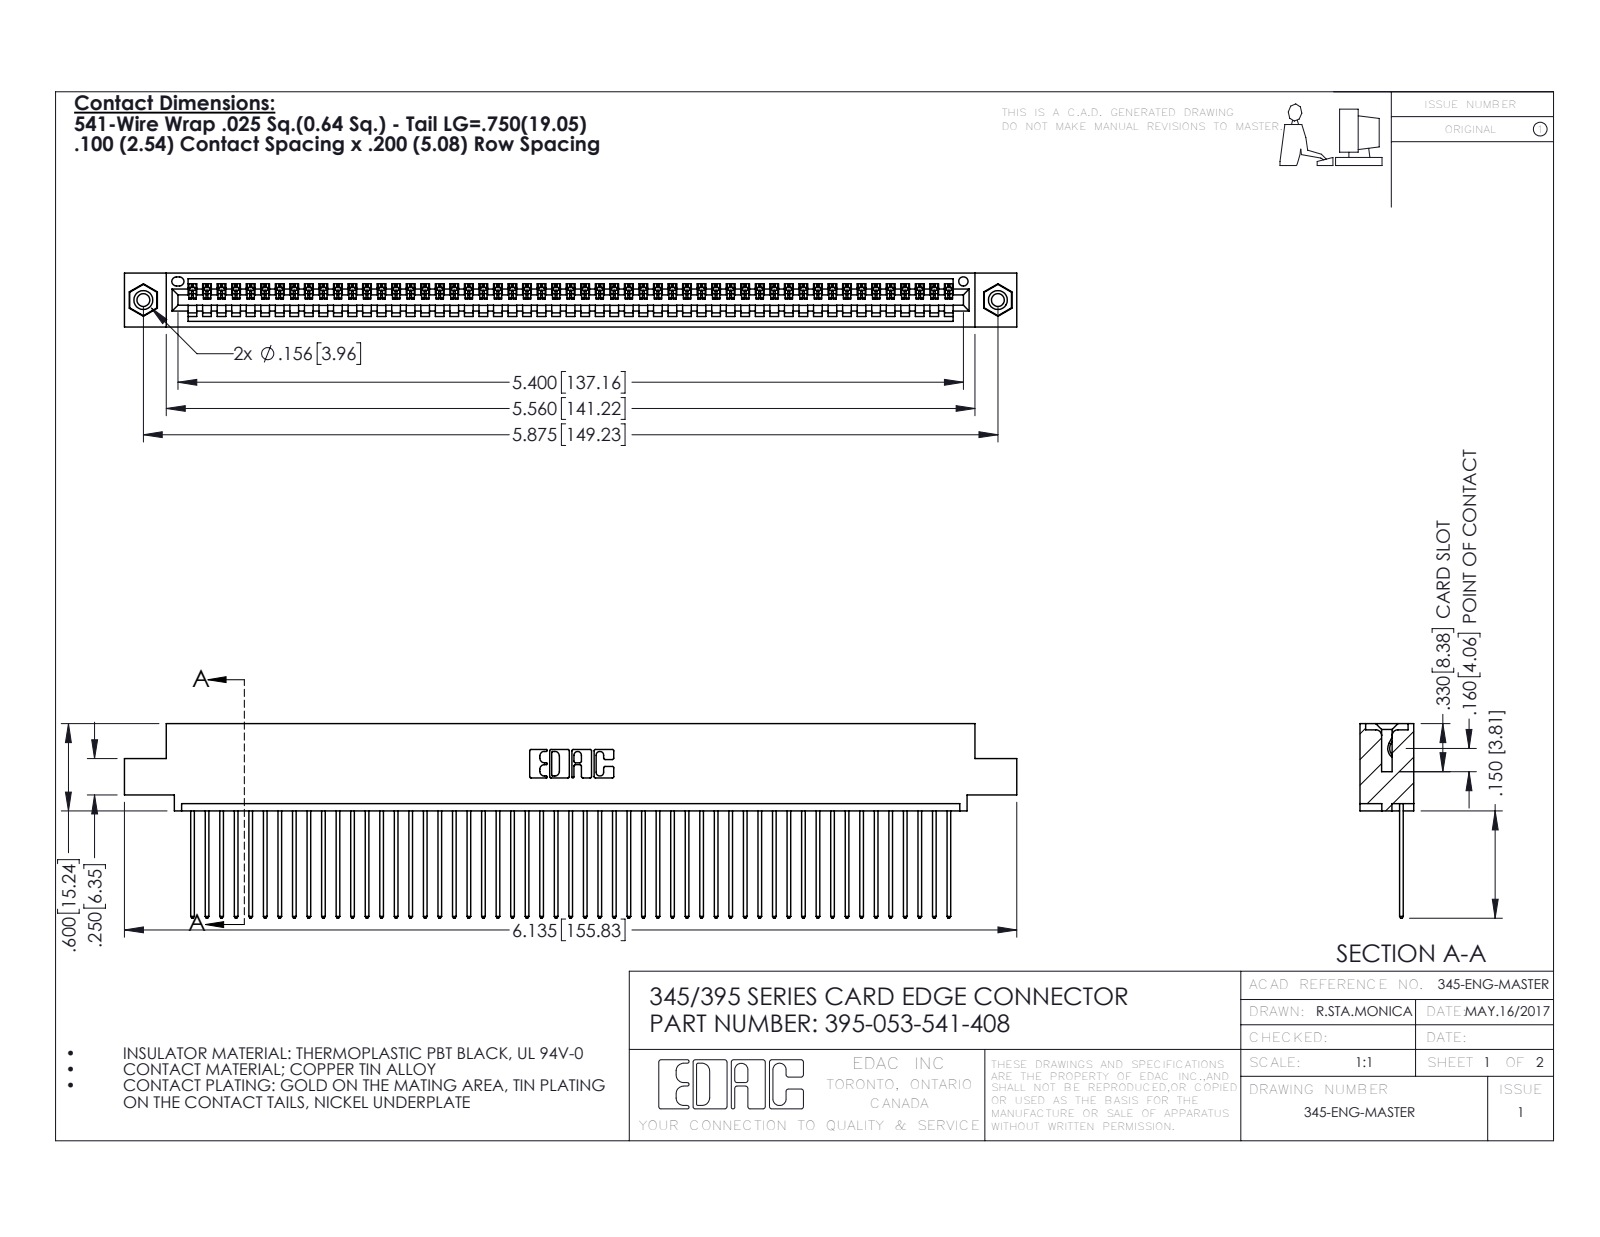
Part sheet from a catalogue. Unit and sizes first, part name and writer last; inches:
Units: inches
Overall size (bounding box): 6.135 × 1.337 × 0.37
Round holes (diameter × count): ⌀0.089 ×2, ⌀0.125 ×2, ⌀0.156 ×2, ⌀0.064 ×1
Round bosses / shafts (diameter × count): ⌀0.155 ×2
Partial cylindrical surfaces — rounded edges, fillets, slot ends (radius × count): R0.006 ×106, R0.01 ×106, R0.01 ×22, R0.007 ×6, R0.031 ×6, R0.026 ×3, R0.031 ×2, R0.04 ×2
Main face-to-face distances: 0.072, 0.298, 0.098, 0.272, 0.025, 0.37, 0.2, 0.225, 0.149, 0.072
Hole centre spacings: 0.27, 5.639, 5.875
Volume: 0.914 in³ · Surface area: 32.85 in²
Bodies: 56 solids, 3264 faces (2236 planar, 1012 cylindrical, 16 other)
Part name (STEP PRODUCT): 345 Part_0.110 Offset - 0.156 Dia-TI; 395-053-541-408; 345-250-001_345-250-003-102; 345-292-001_345-293-141
STEP written by: SolidWorks 2016 (CONFIG_CONTROL_DESIGN)
